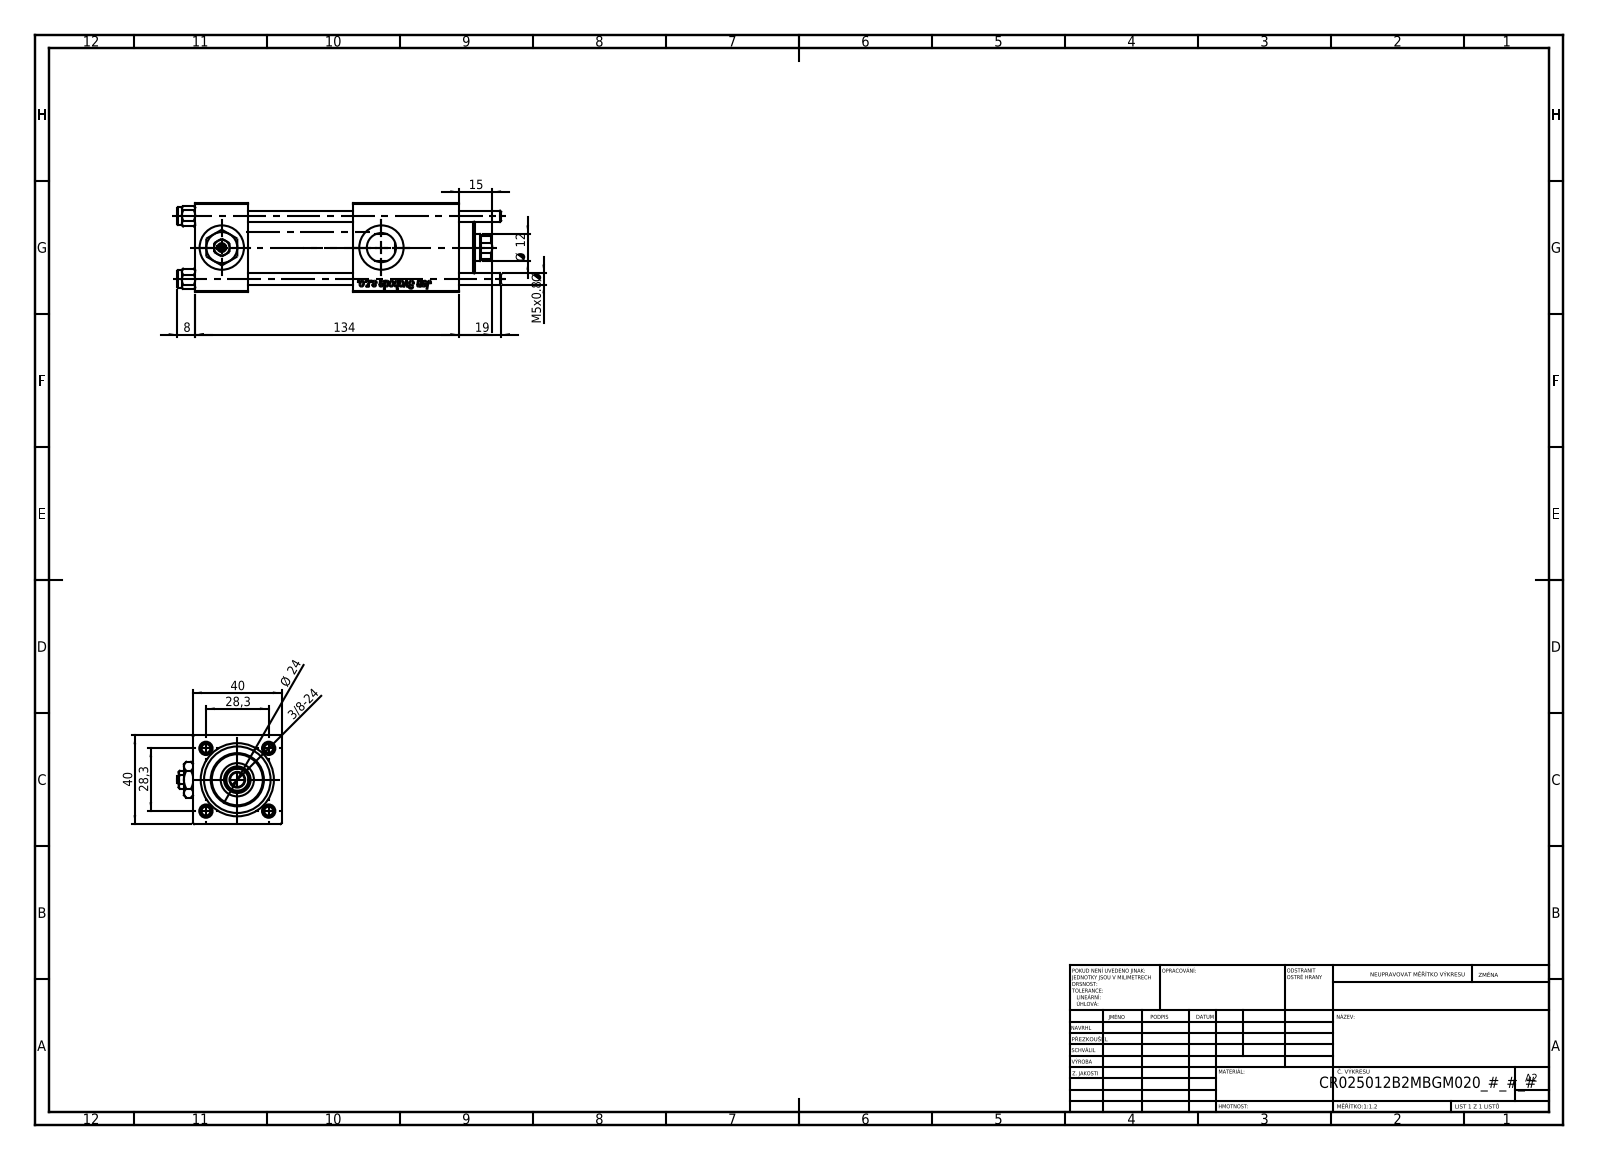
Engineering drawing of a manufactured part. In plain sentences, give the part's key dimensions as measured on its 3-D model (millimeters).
The part is named "V215_VC_A; V215CR_VCP_B; NUT_M5_B; Zatka_pro_OIL_PORT (+2 more)". Its 3-D file was written by "SolidWorks 2019 (CONFIG_CONTROL_DESIGN)". It is 12 solids with 1208 faces: 452 planar, 86 cylindrical and 670 other. Overall it measures 146 by 47 by 40 millimeters. Its volume is 144 131 cubic millimeters and its surface area 59 643 square millimeters. Round holes: 4 of diameter 5, 3 of diameter 20, 2 of diameter 7, 2 of diameter 13.16, 1 of diameter 6.5, 1 of diameter 12, 1 of diameter 15, 1 of diameter 25, 1 of diameter 30. Round bosses or shafts: 4 of diameter 8, 1 of diameter 31, 1 of diameter 24. Partial cylindrical surfaces (rounded edges, fillets, slot ends): 1 of radius 5.5. The main face-to-face distances are 40, 24, 90.3, 66.3, 119, 47, 71, 19.3, 95, 48. The hole center spacings are 20.01, 28.3, 40.02, 72.
